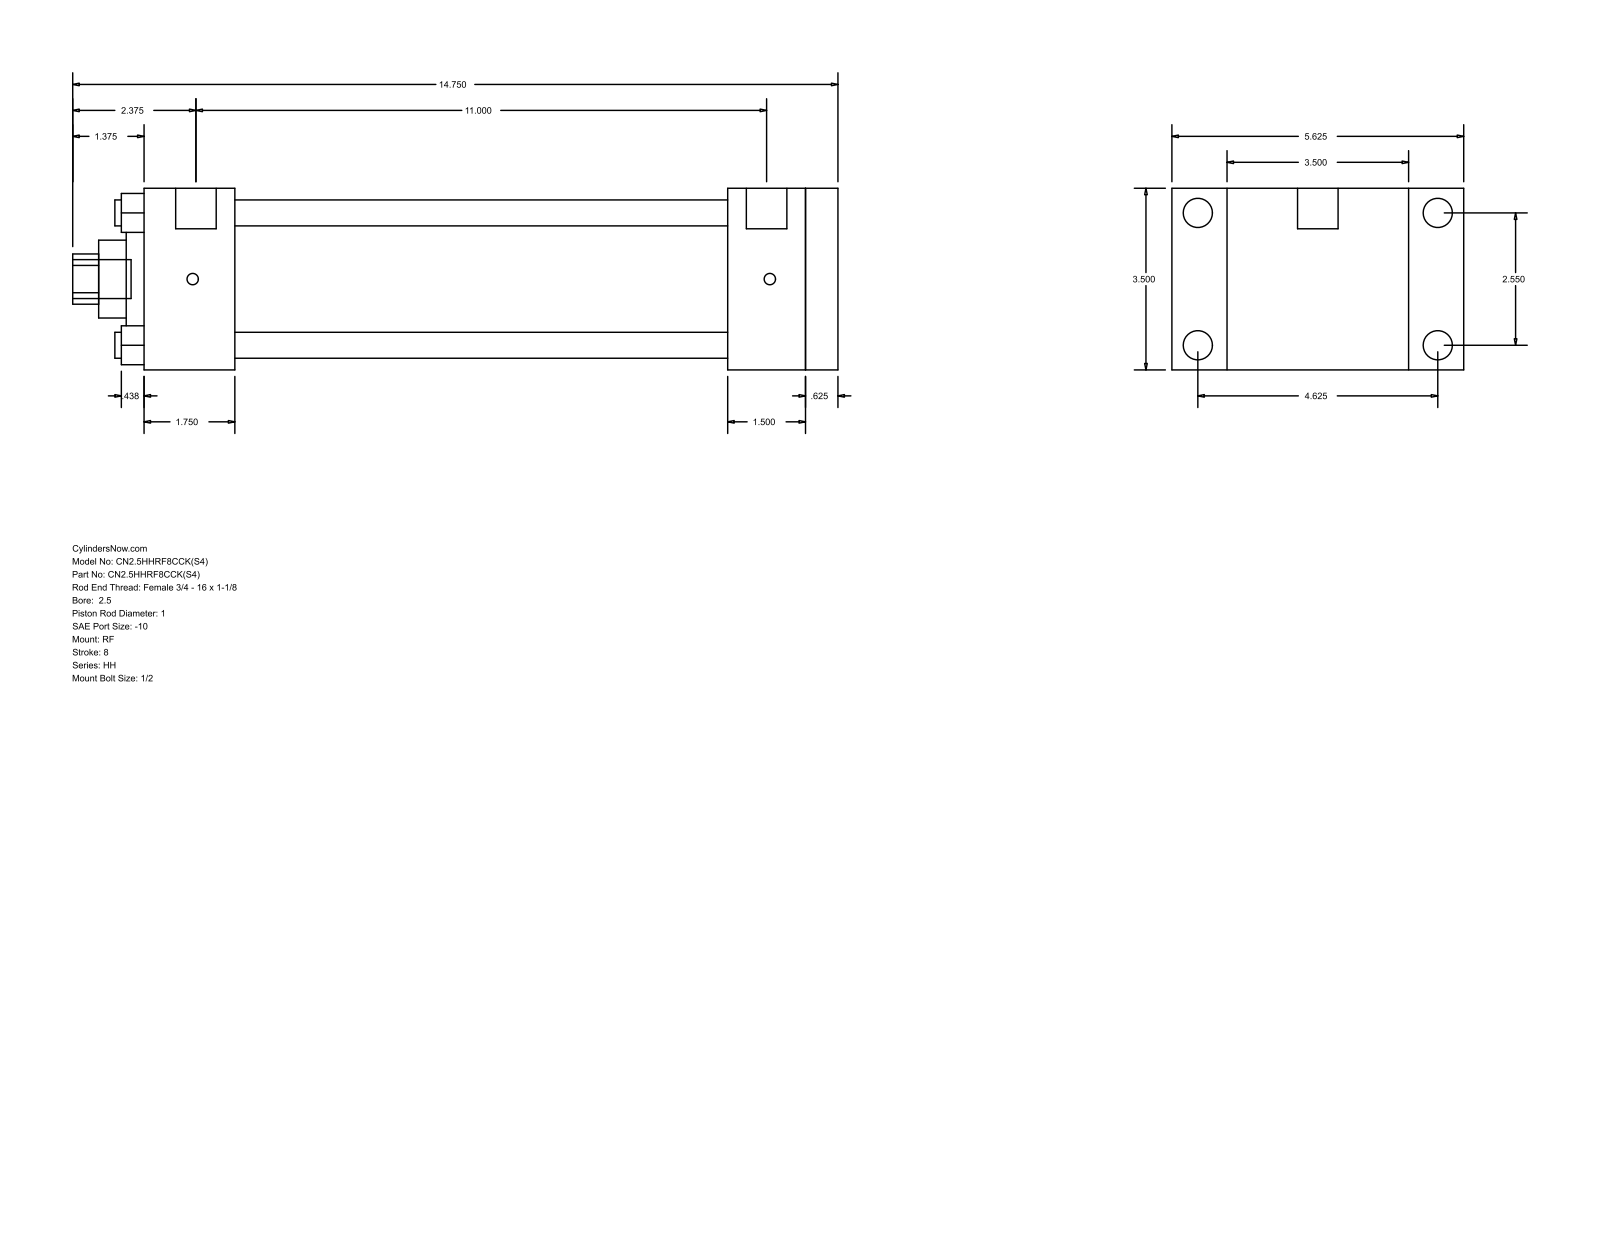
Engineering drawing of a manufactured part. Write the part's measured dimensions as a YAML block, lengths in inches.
part_name: "HH_RF__0250_1"
step_written_by: "GSSL Pune (CONFIG_CONTROL_DESIGN)"
units: inches
bodies: {solids: 0, faces: 94, planar: 65, cylindrical: 29, other: 0}
overall_size: [14.75, 5.625, 3.5]
round_holes:
  - {diameter: 0.5, count: 4}
  - {diameter: 1, count: 1}
  - {diameter: 1.5, count: 1}
  - {diameter: 2.375, count: 1}
  - {diameter: 2.875, count: 1}
round_bosses_or_shafts:
  - {diameter: 0.563, count: 4}
  - {diameter: 0.219, count: 4}
  - {diameter: 0.781, count: 2}
  - {diameter: 0.75, count: 1}
partial_cylinders:
  - {radius: 0.484, count: 1}
face_to_face_distances: [3.5, 0.625, 12.75, 13.375, 1.75, 11, 11.625, 11.25, 9.5, 1.5]
hole_center_spacings: [1.803, 2.55, 3.606]
